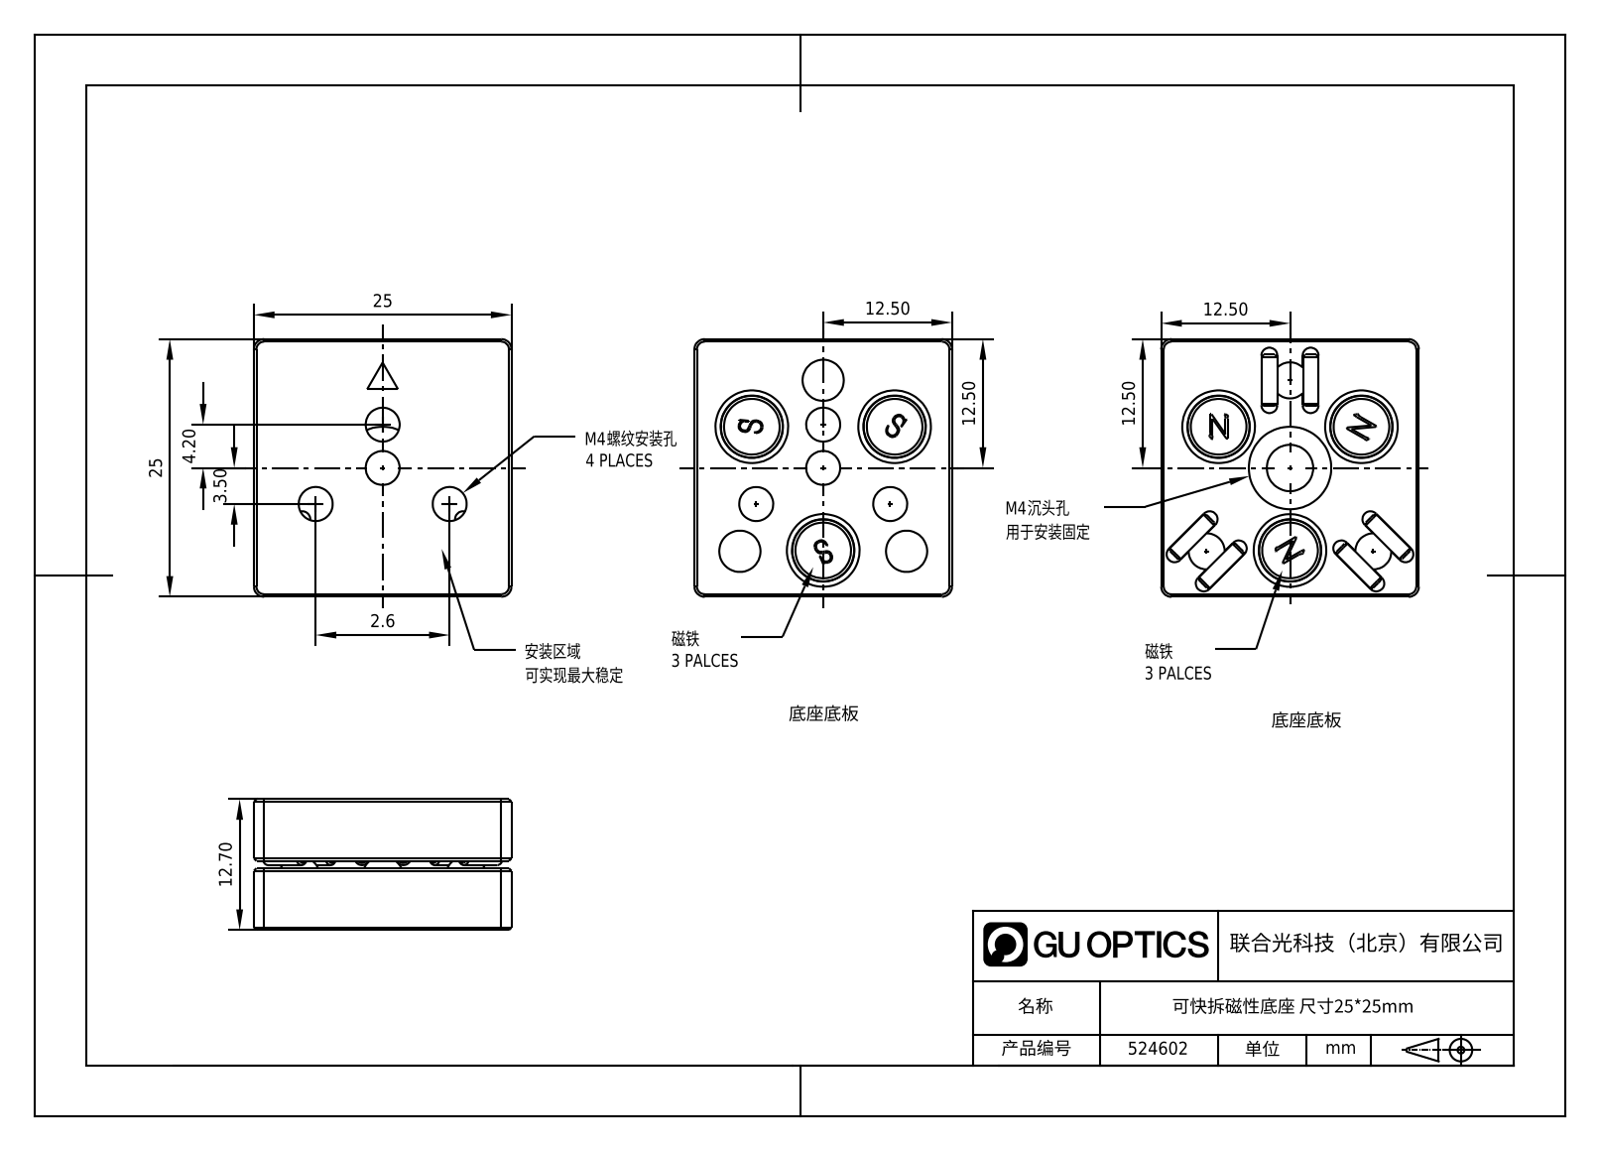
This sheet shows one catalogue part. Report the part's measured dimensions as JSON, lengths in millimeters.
{"part_name": "1.4.6.51_ZGD-K25T_可调光学接杆底座，尺寸25mmx25mm，带M4螺纹孔", "step_written_by": "SolidWorks 2018 (CONFIG_CONTROL_DESIGN)", "units": "millimeters", "bodies": {"solids": 0, "faces": 104, "planar": 42, "cylindrical": 38, "other": 24}, "overall_size": [25, 25, 12.7], "round_holes": [[3.3, 4], [4.5, 1], [8, 1]], "round_bosses_or_shafts": [[1.5, 4]], "partial_cylinders_radius": [[0.78, 6], [1, 4]], "face_to_face_distances": [6, 6.7, 12.7, 25, 0.7, 4.74, 21.56, 26.3, 16.82, 9.73], "hole_center_spacings": [7.38, 10.08, 4.2, 13]}
